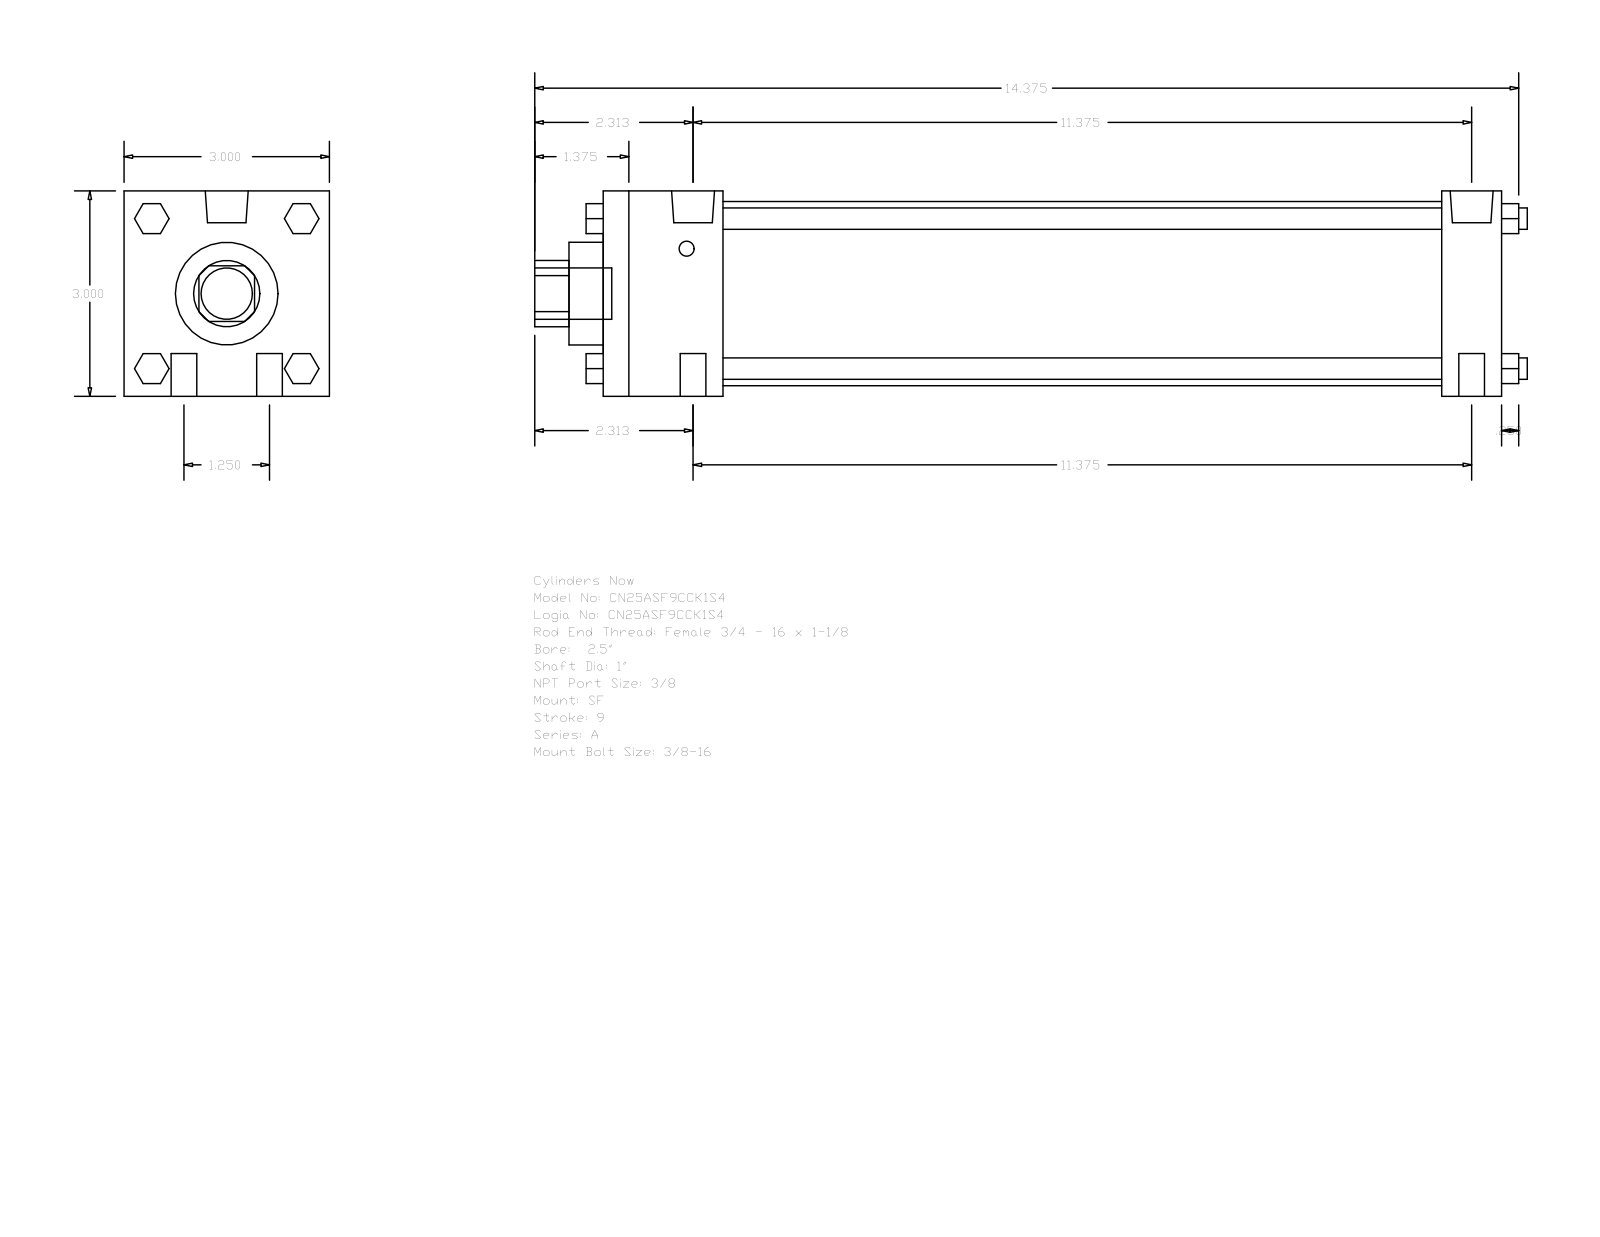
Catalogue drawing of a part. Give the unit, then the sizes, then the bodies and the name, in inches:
Units: inches
Overall size (bounding box): 14.5 × 3 × 3
Round holes (diameter × count): ⌀1 ×1, ⌀1.5 ×1, ⌀2.69 ×1
Round bosses / shafts (diameter × count): ⌀0.375 ×4, ⌀0.313 ×4, ⌀0.627 ×2, ⌀0.219 ×2, ⌀0.75 ×1
Partial cylindrical surfaces — rounded edges, fillets, slot ends (radius × count): R0.484 ×1
Main face-to-face distances: 3, 13.125, 12.25, 0.875, 1.75, 10.5, 11.375, 0.5, 13.625, 0.25
Bodies: 0 solids, 124 faces (94 planar, 30 cylindrical, 0 other)
Part name (STEP PRODUCT): A_SF__0250_1
STEP written by: GSSL Pune (CONFIG_CONTROL_DESIGN)
